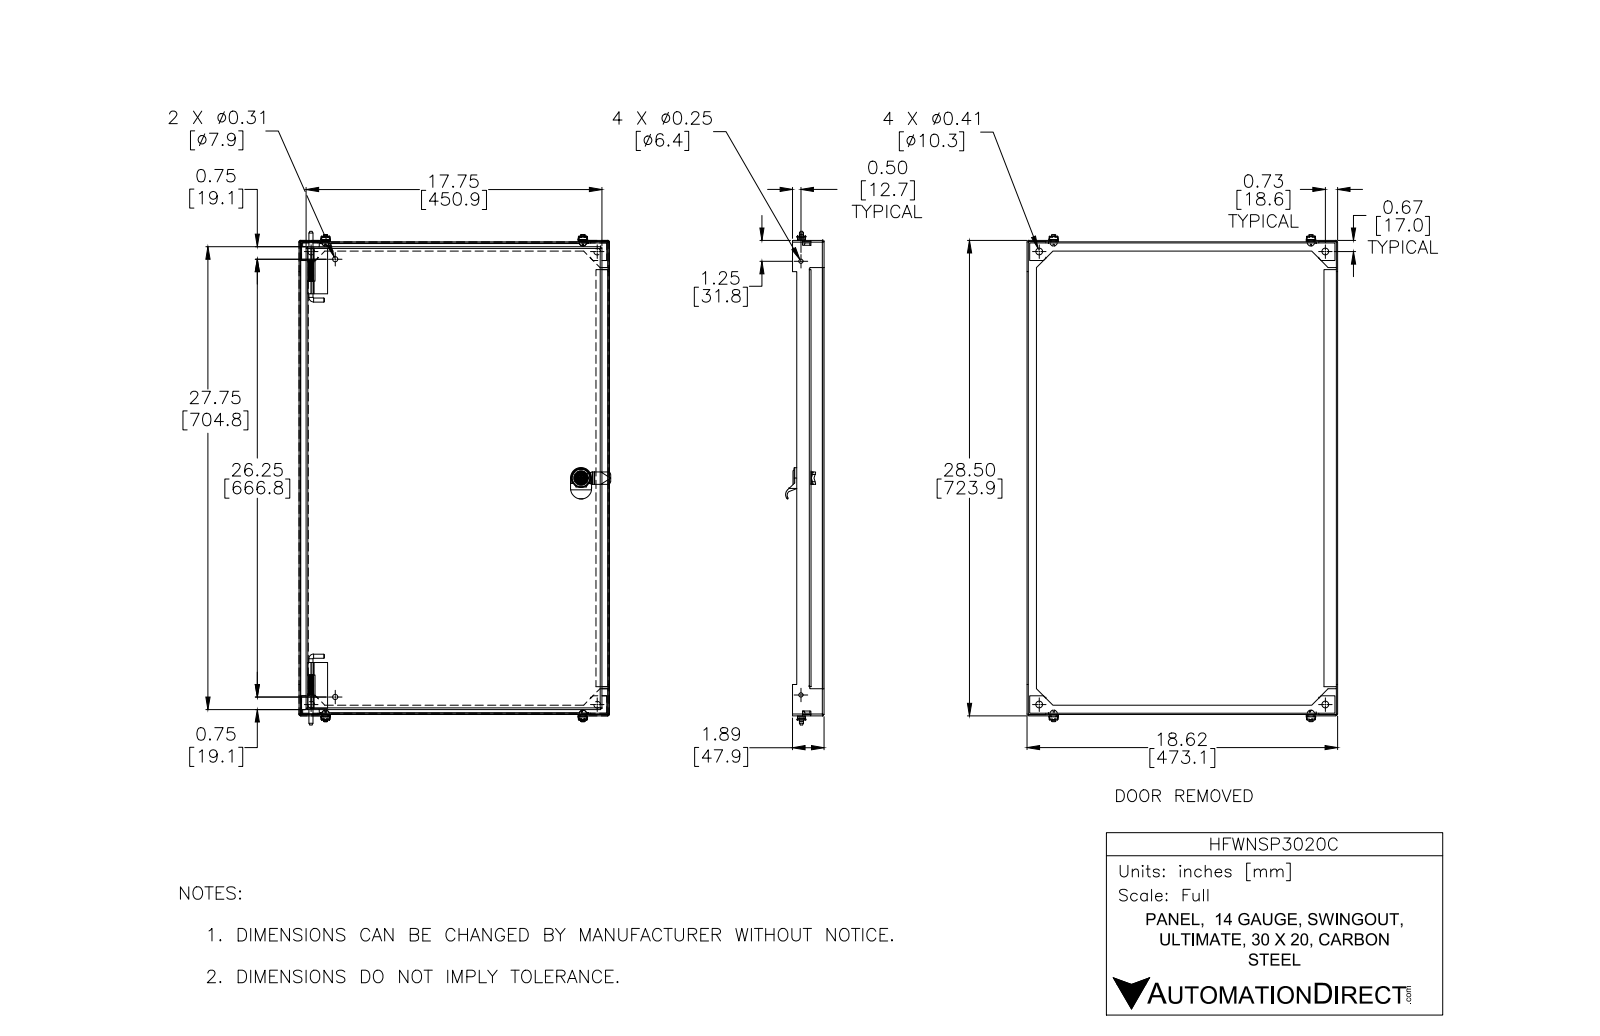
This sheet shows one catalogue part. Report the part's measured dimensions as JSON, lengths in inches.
{"part_name": "HFWNSP30CBKLS; HFW328156; 1-100-1-1; 200-9113(1-142-P9)_GDZn verchromt (+8 more)", "step_written_by": "SolidWorks 2014 (AUTOMOTIVE_DESIGN)", "units": "inches", "bodies": {"solids": 28, "faces": 1243, "planar": 623, "cylindrical": 388, "other": 232}, "overall_size": [29.601, 18.697, 2.306], "volume_in3": 58.03, "surface_area_in2": 1584, "round_holes": [[0.25, 5], [0.406, 4], [0.185, 3], [0.313, 3], [0.328, 3], [0.281, 2], [0.163, 1], [0.261, 1], [0.295, 1], [0.394, 1], [0.524, 1], [0.634, 1]], "round_bosses_or_shafts": [[0.25, 4], [1.26, 1], [1.102, 1], [1, 1], [0.945, 1], [0.768, 1], [0.63, 1], [0.531, 1]], "partial_cylinders_radius": [[0.025, 36], [0.045, 22], [0.031, 13], [0.105, 13], [0.021, 12], [0.021, 6], [0.157, 4], [0.031, 2]], "face_to_face_distances": [0.074, 28.27, 1.489, 1.563, 18.551, 0.297, 27.973, 0.425, 18.126, 18.101], "hole_center_spacings": [15.437, 0.875, 1.513, 13.614, 15.724, 16.312, 17.16, 19.744]}
